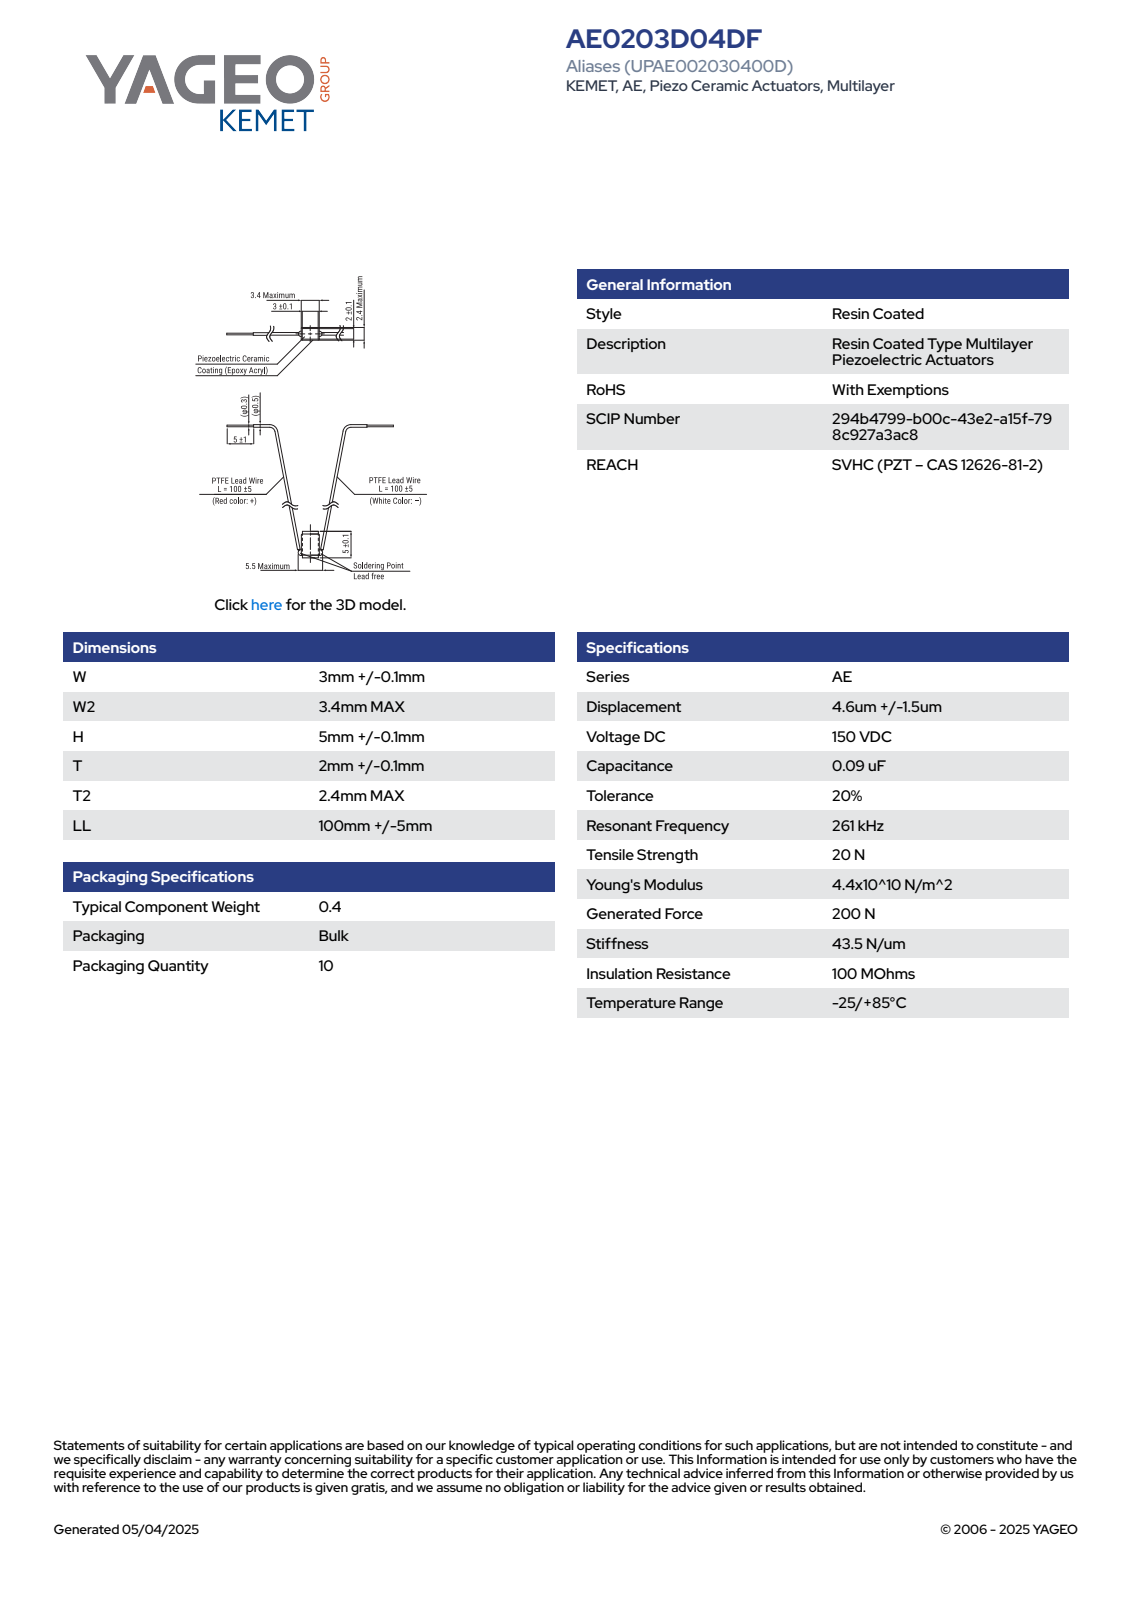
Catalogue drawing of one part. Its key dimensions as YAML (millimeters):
part_name: "AL_KAE1_W3.1W23.4H5.1T2.1T22.4"
step_written_by: "SolidWorks 2014 (AUTOMOTIVE_DESIGN)"
units: millimeters
bodies: {solids: 4, faces: 93, planar: 85, cylindrical: 8, other: 0}
overall_size: [5.11, 3.4, 2.4]
volume: 34
surface_area: 75
partial_cylinders:
  - {radius: 0.15, count: 8}
face_to_face_distances: [2.25, 3, 2.1, 5.1, 2.9, 2.4, 3.1, 0.5, 2.05, 3.05]
